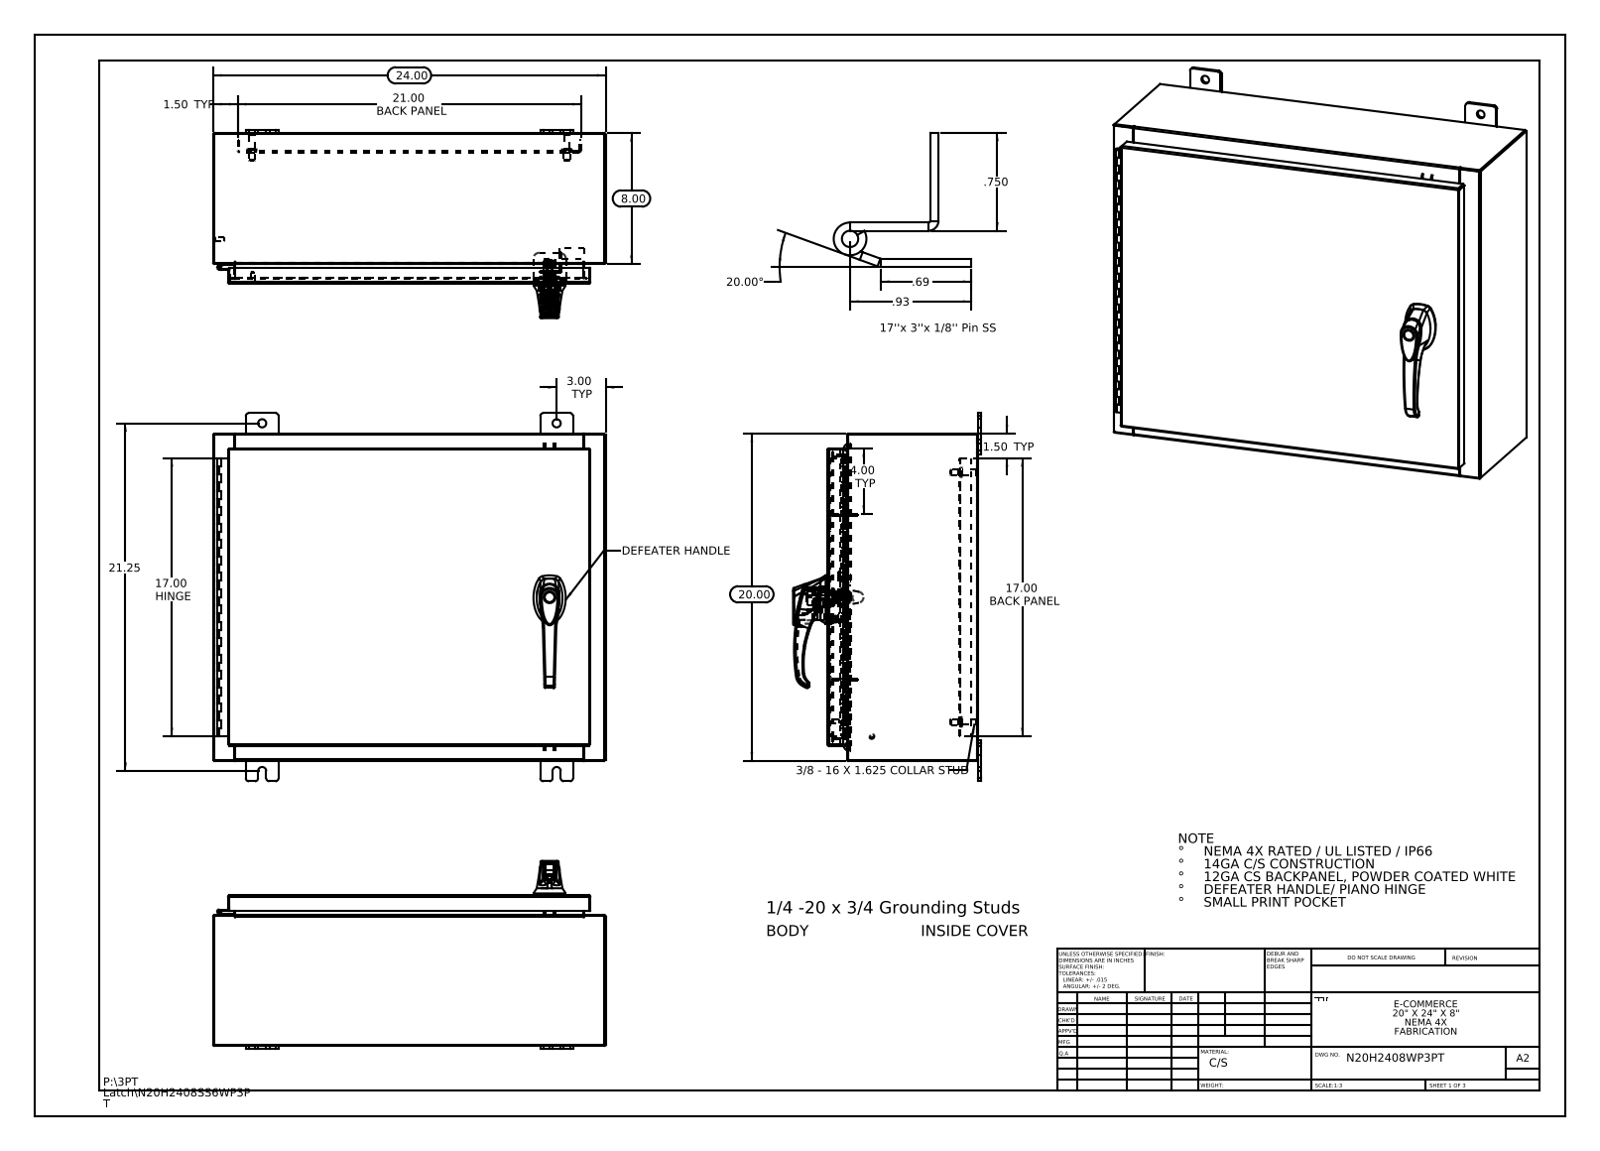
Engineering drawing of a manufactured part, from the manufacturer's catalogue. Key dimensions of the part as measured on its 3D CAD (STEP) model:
Part name (STEP PRODUCT): N20H2408SS6WP3PT Bottom; 297025; N20H2408SS6WP3PT Body; 033060_032151 (+8 more)
STEP written by: SolidWorks 2013 (CONFIG_CONTROL_DESIGN)
Units: inches
Bodies: 37 solids, 2402 faces (835 planar, 869 cylindrical, 698 other)
Overall size (bounding box): 24 × 22.5 × 11.495
Volume: 192.7 in³ · Surface area: 4 762 in²
Round holes (diameter × count): ⌀0.5 ×8, ⌀0.25 ×4, ⌀0.138 ×3, ⌀0.161 ×3, ⌀0.079 ×2, ⌀0.203 ×2, ⌀0.313 ×2, ⌀0.437 ×2, ⌀0.125 ×1, ⌀0.125 ×1, ⌀0.197 ×1, ⌀0.276 ×1
Round bosses / shafts (diameter × count): ⌀0.625 ×4, ⌀0.375 ×4, ⌀0.33 ×4, ⌀0.157 ×4, ⌀0.14 ×4, ⌀0.315 ×3, ⌀0.236 ×3, ⌀1.181 ×1
Partial cylindrical surfaces — rounded edges, fillets, slot ends (radius × count): R0.118 ×37, R0.006 ×33, R0.19 ×24, R0.013 ×22, R0.088 ×18, R0.039 ×15, R0.028 ×12, R0.008 ×6
Main face-to-face distances: 0.075, 9.126, 9.051, 9.201, 0.104, 19.925, 1, 1.075, 8.051, 8.126
Hole centre spacings: 3.404, 0.295, 0.625, 0.841, 1.25, 1.313, 1.561, 1.858
